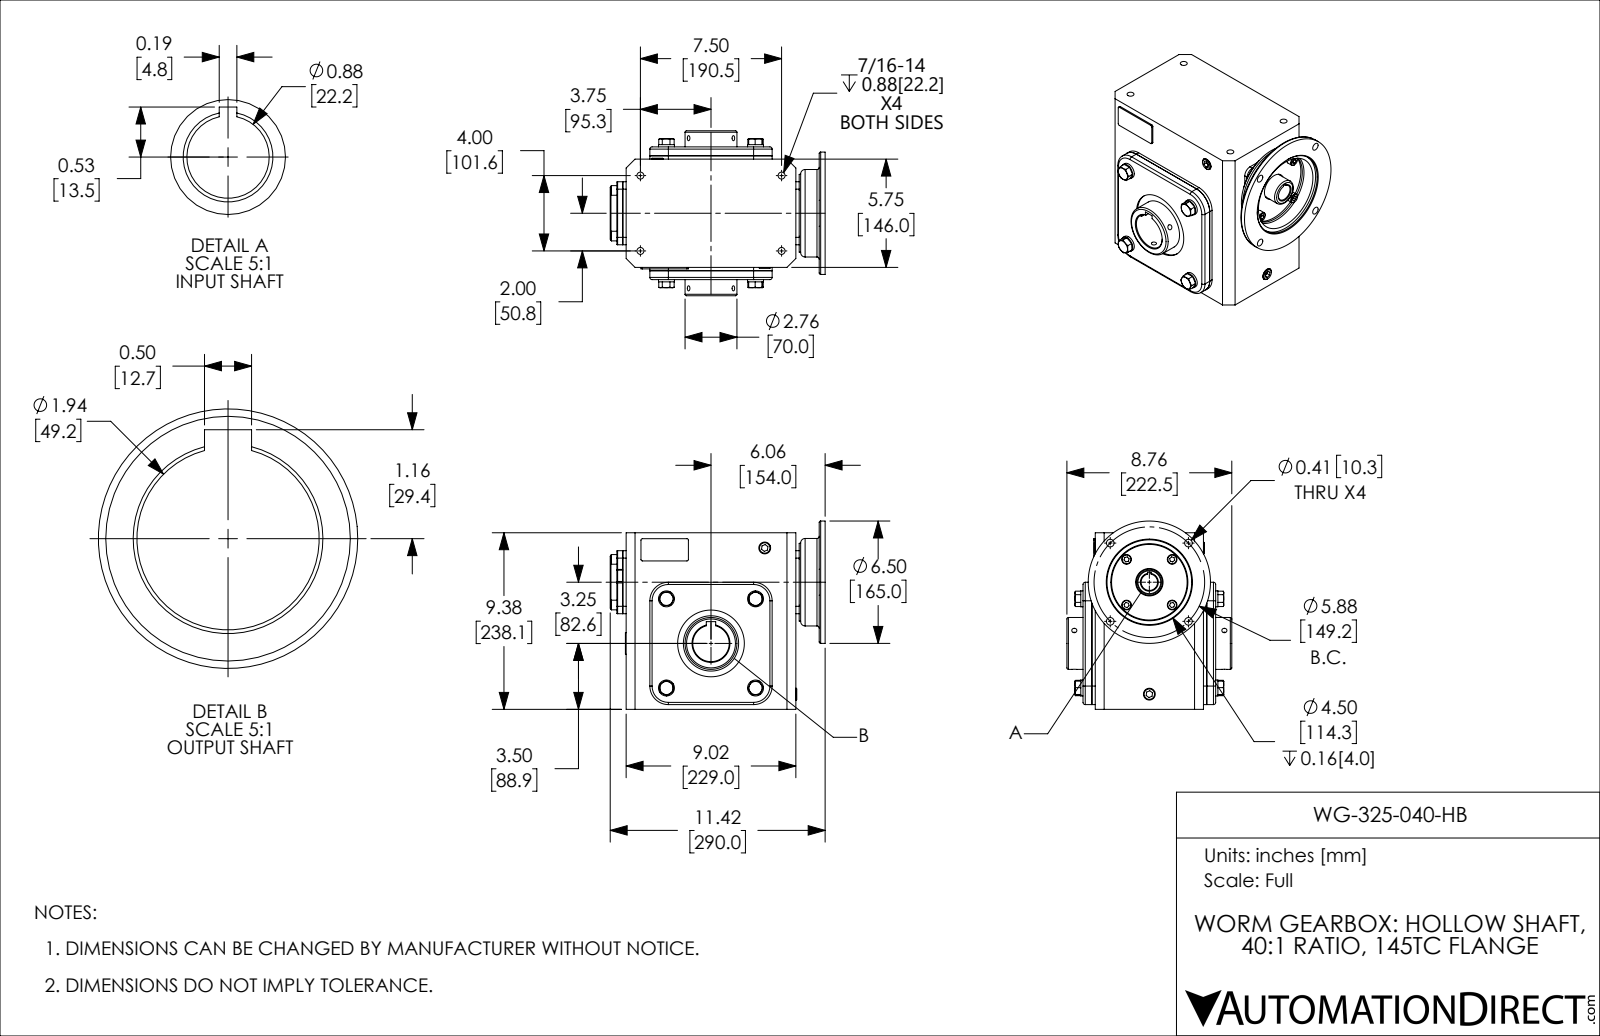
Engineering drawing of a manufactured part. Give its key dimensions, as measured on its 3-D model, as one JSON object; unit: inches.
{"part_name": "WG-325-040-HB", "step_written_by": "SolidWorks 2017 (AUTOMOTIVE_DESIGN)", "units": "inches", "bodies": {"solids": 39, "faces": 587, "planar": 314, "cylindrical": 178, "other": 95}, "overall_size": [11.417, 9.998, 8.76], "volume_in3": 516.3, "surface_area_in2": 987.3, "round_holes": [[0.272, 6], [0.368, 4], [0.406, 4], [0.628, 3], [0.591, 1], [0.875, 1], [0.978, 1], [1.181, 1], [1.457, 1], [1.937, 1], [2.441, 1], [2.756, 1]], "round_bosses_or_shafts": [[0.846, 4], [0.512, 4], [6.496, 1], [4.646, 1], [4.134, 1], [2.835, 1], [1.378, 1], [1.142, 1]], "partial_cylinders_radius": [[0.118, 8], [0.079, 7], [0.394, 4], [0.906, 4], [0.984, 4], [0.02, 2], [0.039, 2]], "face_to_face_distances": [0.079, 0.177, 6.496, 0.394, 0.571, 6.319, 5.925, 6.398, 0.65, 0.472], "hole_center_spacings": [2.937, 4.154, 4.244, 7.064, 7.972, 2.385, 4, 4.389]}
